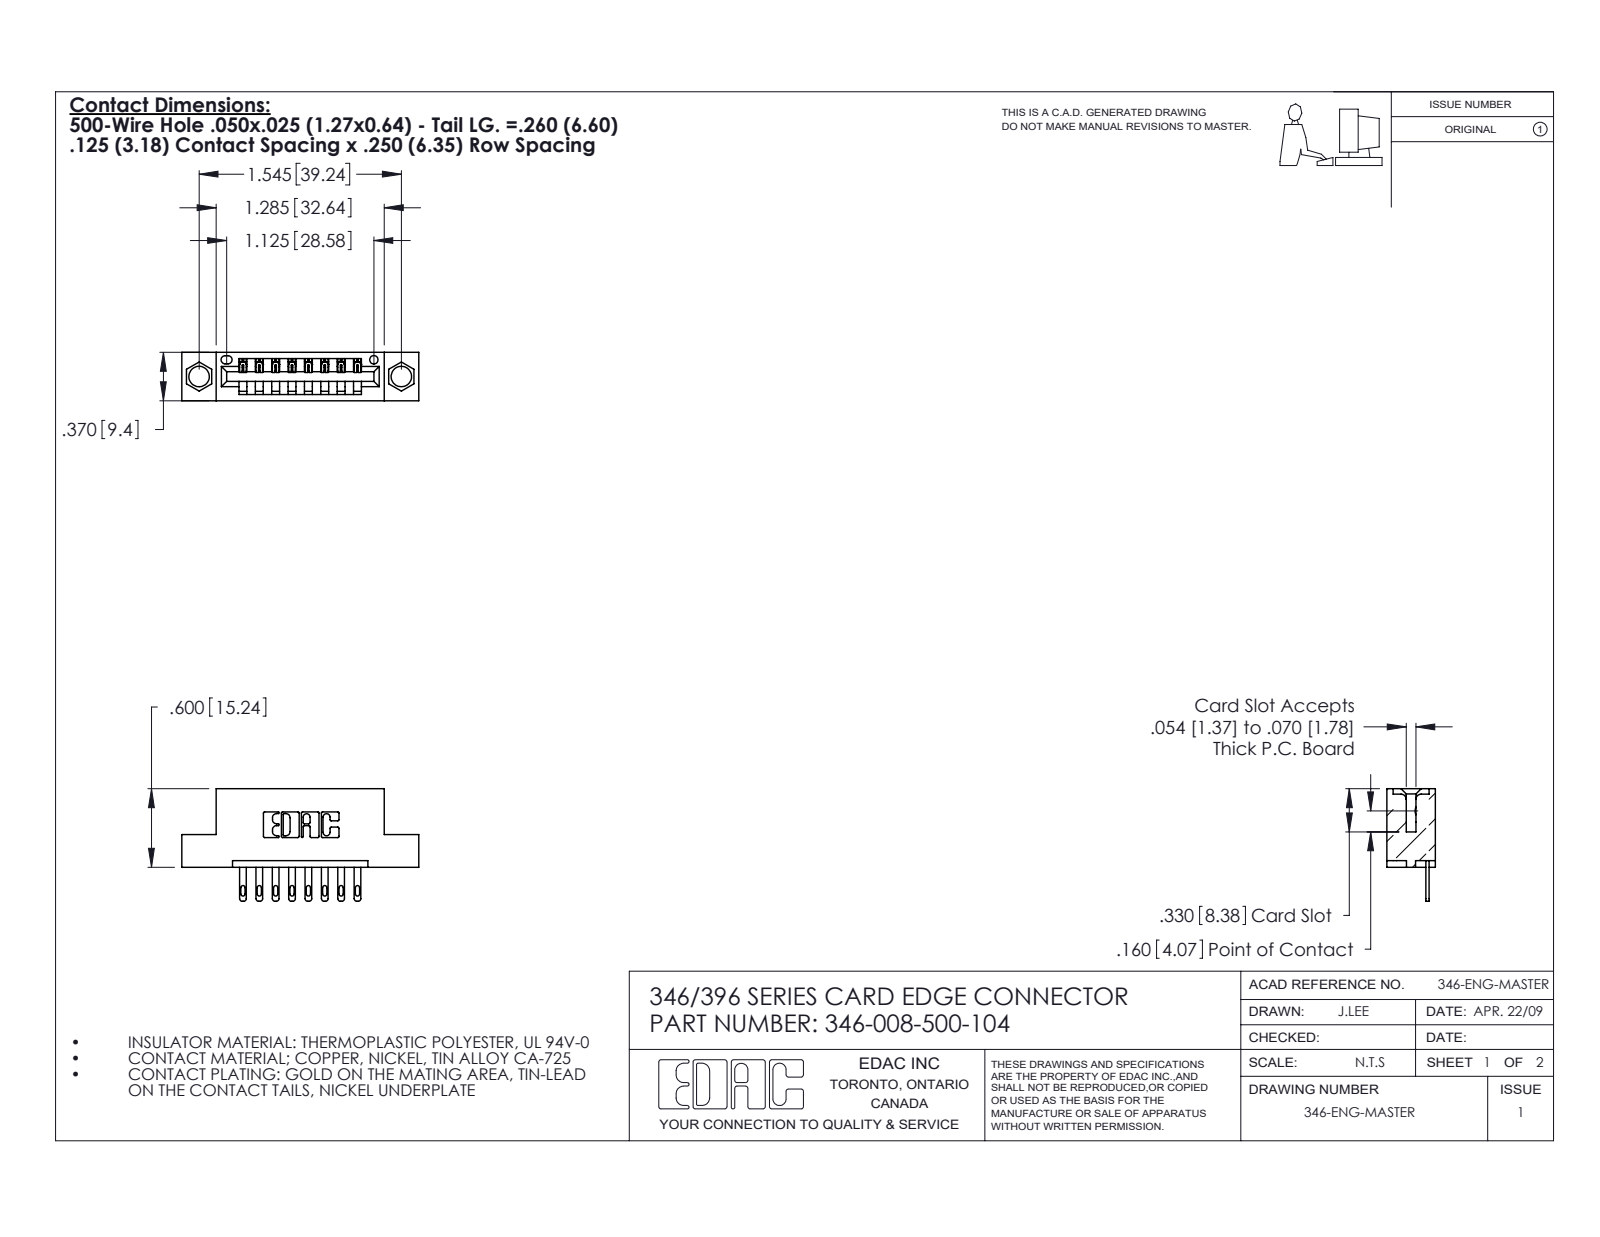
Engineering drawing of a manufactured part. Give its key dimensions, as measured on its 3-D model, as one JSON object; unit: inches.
{"part_name": "346 Part_Flush Mounting Lugs - 0.156 Dia-TH; 345-292-001_345-293-100; 346-008-500-104", "step_written_by": "SolidWorks 2020 (CONFIG_CONTROL_DESIGN)", "units": "inches", "bodies": {"solids": 9, "faces": 568, "planar": 362, "cylindrical": 206, "other": 0}, "overall_size": [1.81, 0.86, 0.37], "volume_in3": 0.248, "surface_area_in2": 7.084, "round_holes": [[0.156, 2], [0.064, 1]], "partial_cylinders_radius": [[0.01, 22], [0.006, 16], [0.016, 16], [0.02, 16], [0.007, 6], [0.031, 6], [0.026, 3], [0.031, 2]], "face_to_face_distances": [0.25, 0.37, 0.048, 0.322, 0.5, 0.072, 0.298, 0.025, 0.148, 0.222], "hole_center_spacings": [0.246, 1.341, 1.545]}
